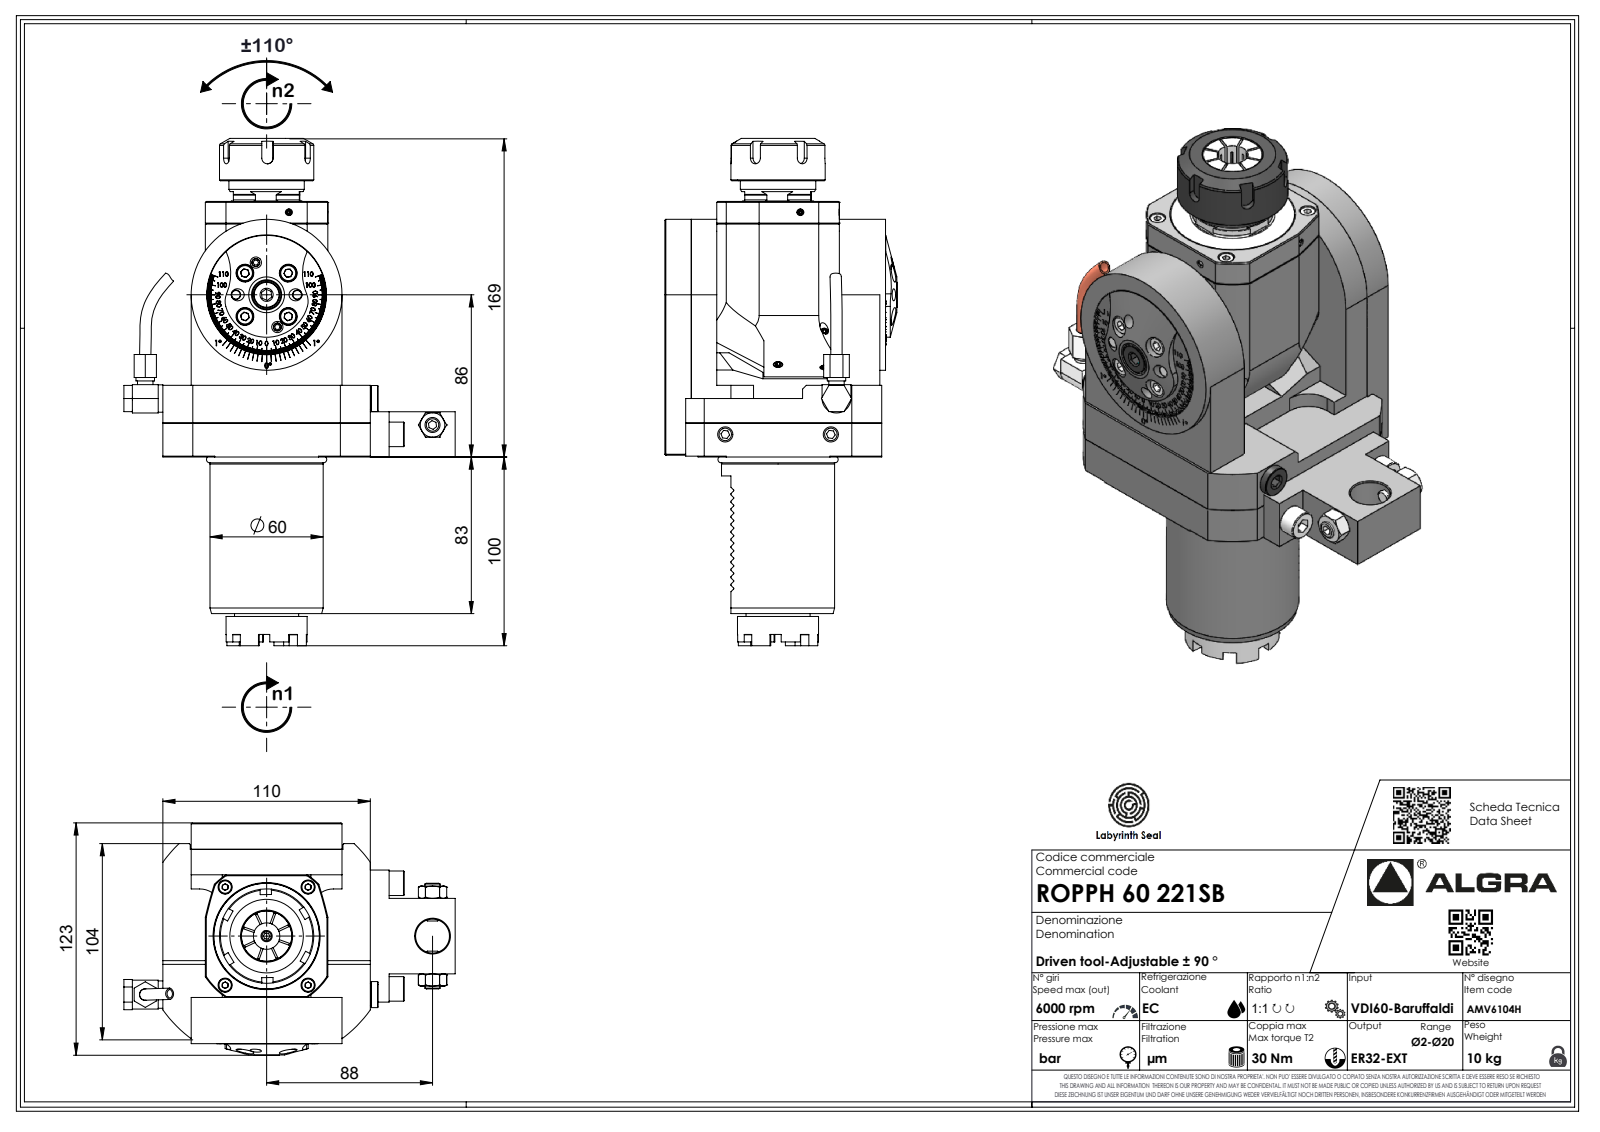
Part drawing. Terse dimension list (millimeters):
name: ROPPH60221SB
written by: SolidWorks 2023 (AUTOMOTIVE_DESIGN)
unit: mm
bodies: 1 solid, 664 faces (429 planar, 115 cylindrical, 120 other)
size: 268.91 × 175.7 × 123
volume: 1 468 000 mm³; area: 125 873 mm²
holes: 1× ⌀2.1
bosses: 1× ⌀80, 1× ⌀60, 1× ⌀58.7, 1× ⌀50, 1× ⌀43, 1× ⌀40, 1× ⌀34, 1× ⌀14.5
rounds: 19× R0.2, 14× R0.3, 7× R0.33, 7× R0.52, 7× R3.7, 5× R3, 2× R10, 2× R12
face distances: 22.5, 87.5, 65, 80, 7.5, 95, 7, 15, 27.5, 72.5
